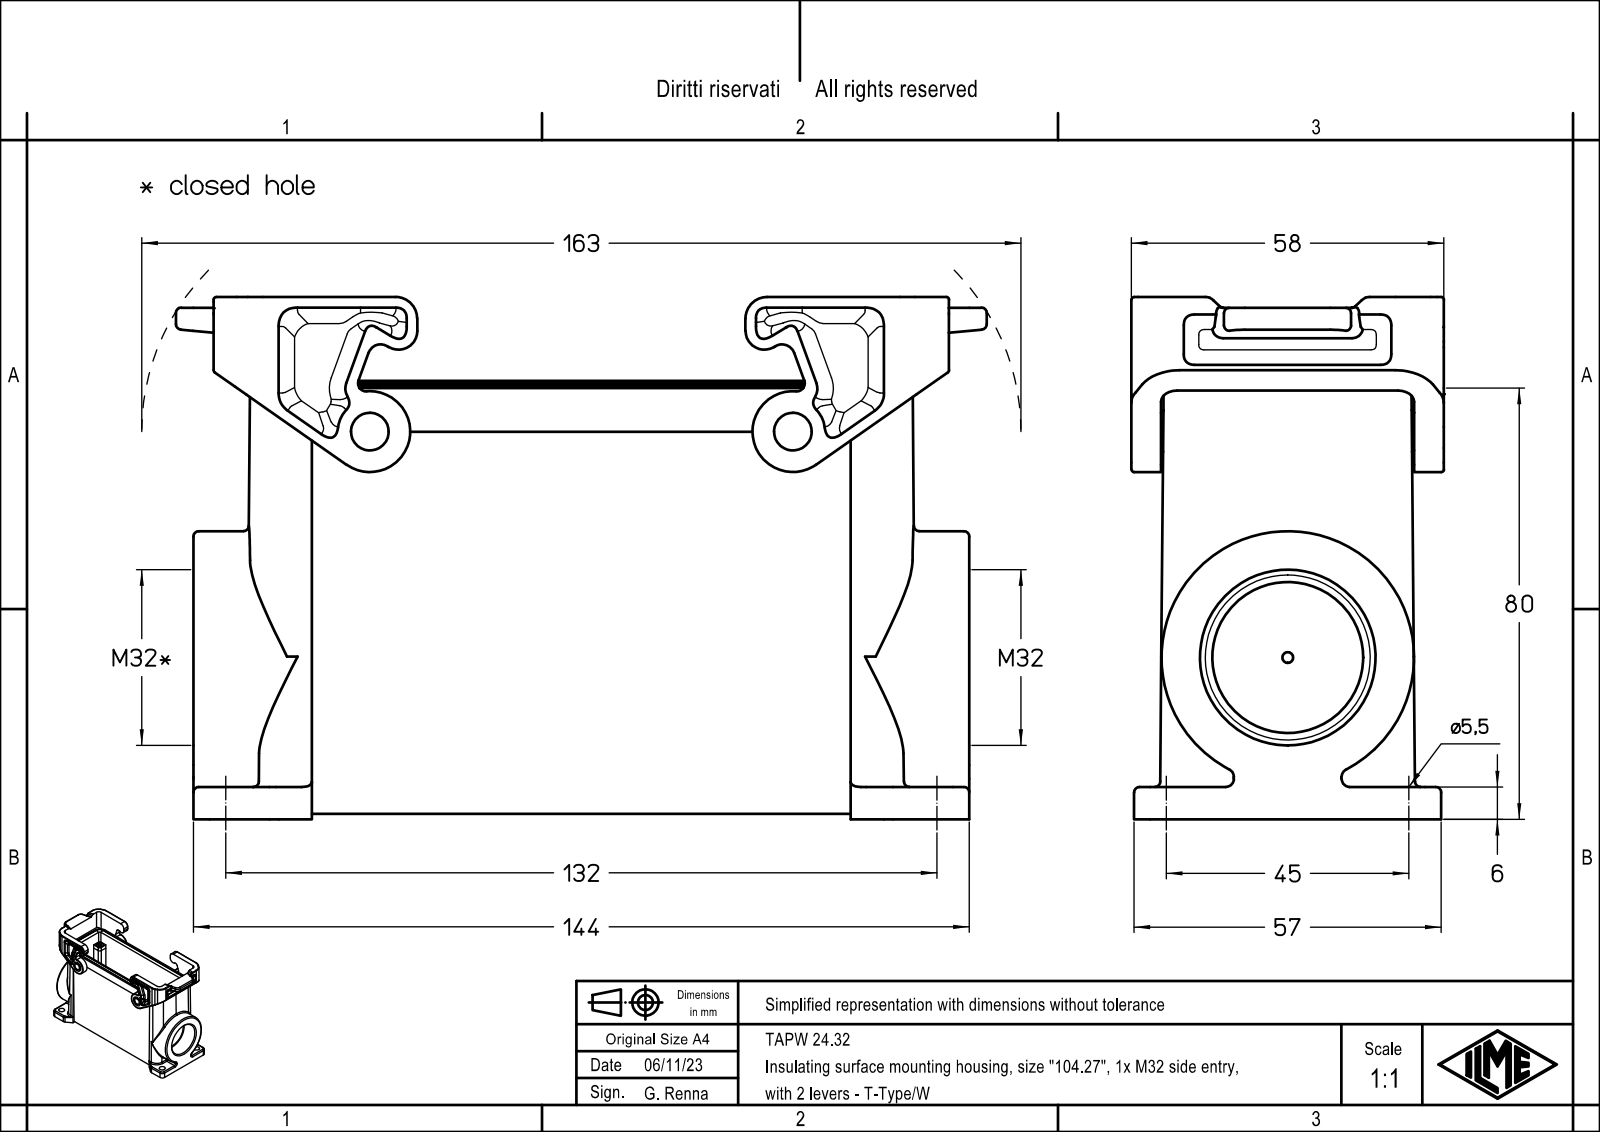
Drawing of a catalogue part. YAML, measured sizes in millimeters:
part_name: "TAPW 24.32"
step_written_by: "Creo Elements/Direct Modeling 20.1B 02-Apr-2019 (C) Parametric Technology GmbH (AUTOMOTIVE_DESIGN)"
units: millimeters
bodies: {solids: 1, faces: 414, planar: 204, cylindrical: 158, other: 52}
overall_size: [150.5, 96.9, 58]
volume: 228695
surface_area: 80522
round_holes:
  - {diameter: 5.5, count: 4}
  - {diameter: 28, count: 1}
  - {diameter: 30.6, count: 1}
round_bosses_or_shafts:
  - {diameter: 7, count: 2}
  - {diameter: 46.87, count: 1}
partial_cylinders:
  - {radius: 3, count: 20}
  - {radius: 1, count: 16}
  - {radius: 2, count: 16}
  - {radius: 1.5, count: 10}
  - {radius: 1.3, count: 8}
  - {radius: 6, count: 8}
  - {radius: 7, count: 8}
  - {radius: 4, count: 6}
face_to_face_distances: [35.2, 5.5, 5.9, 41.1, 1, 6.5, 11.4, 46.6, 52.5, 5]
hole_center_spacings: [45, 132, 139.46]
